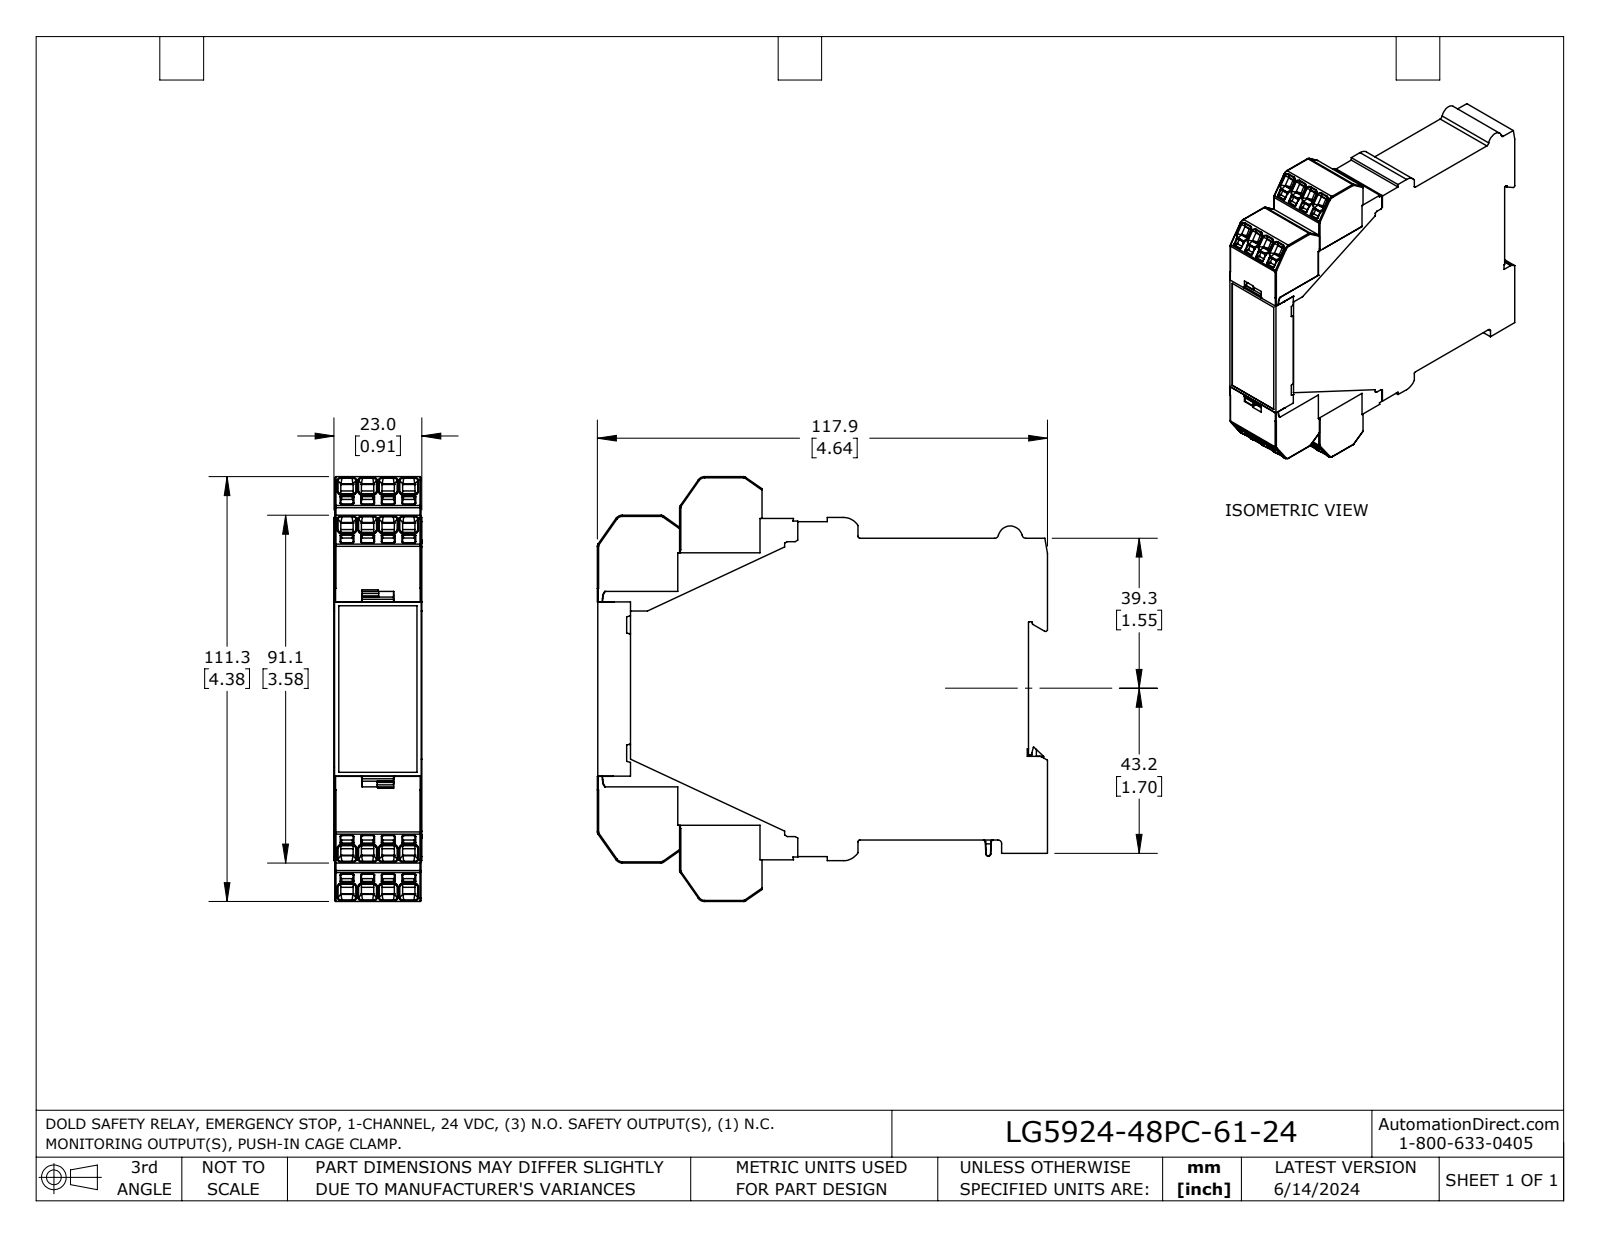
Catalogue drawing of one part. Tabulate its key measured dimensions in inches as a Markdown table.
| quantity | value |
| --- | --- |
| part name | LG5924 |
| STEP written by | SolidWorks 2023 (AUTOMOTIVE_DESIGN) |
| units | inches |
| bodies | 18 solids, 1620 faces (1027 planar, 335 cylindrical, 258 other) |
| overall size | 4.646 × 4.38 × 0.906 |
| volume | 14.93 in³ |
| surface area | 76.56 in² |
| round holes (diameter × count) | 0.067 × 4, 0.049 × 1 |
| round bosses / shafts (diameter × count) | 0.053 × 1 |
| partial cylindrical surfaces (radius × count) | 0.008 × 127, 0.008 × 32, 0.012 × 28, 0.039 × 16, 0.004 × 10, 0.02 × 7, 0.005 × 6, 0.004 × 4 |
| main face-to-face distances | 0.906, 0.898, 0.398, 0.9, 0.892, 0.848, 2.412, 2.96, 0.15, 0.548 |
| hole center spacings | 0.638, 0.848, 1.061 |
